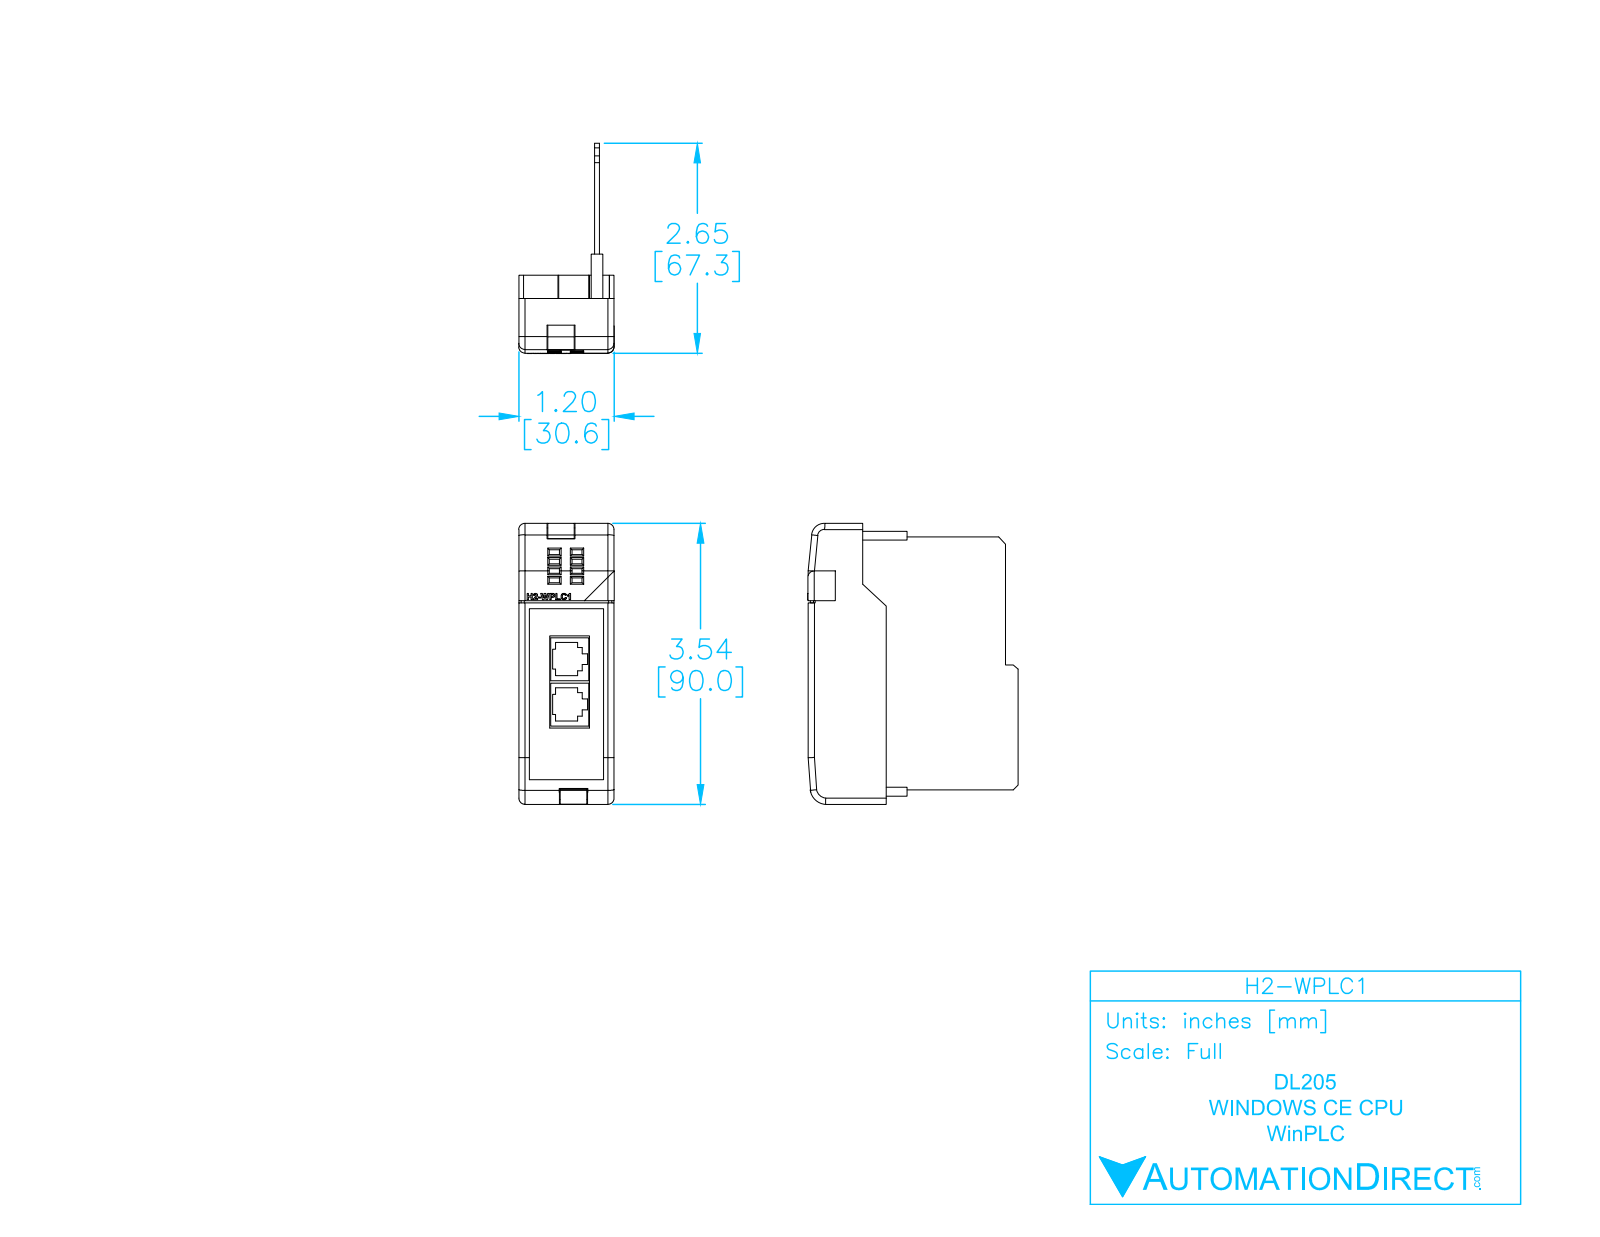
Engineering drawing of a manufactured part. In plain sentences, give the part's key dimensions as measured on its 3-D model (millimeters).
The part is named "H2-WPLC1". Its 3-D file was written by "SolidWorks 2009 (AUTOMOTIVE_DESIGN)". It is 4 solids with 402 faces: 282 planar, 84 cylindrical and 36 other. Overall it measures 90 by 67.38 by 30.55 millimeters. Its volume is 19 329 cubic millimeters and its surface area 29 785 square millimeters. Partial cylindrical surfaces (rounded edges, fillets, slot ends): 28 of radius 0.5, 11 of radius 2, 4 of radius 0.25, 2 of radius 1, 1 of radius 2.62, 1 of radius 3.79, 1 of radius 4.12, 1 of radius 5.29. The main face-to-face distances are 1.5, 4.72, 3.22, 6.22, 24.28, 29, 0.5, 25.78, 30.5, 22.78.
